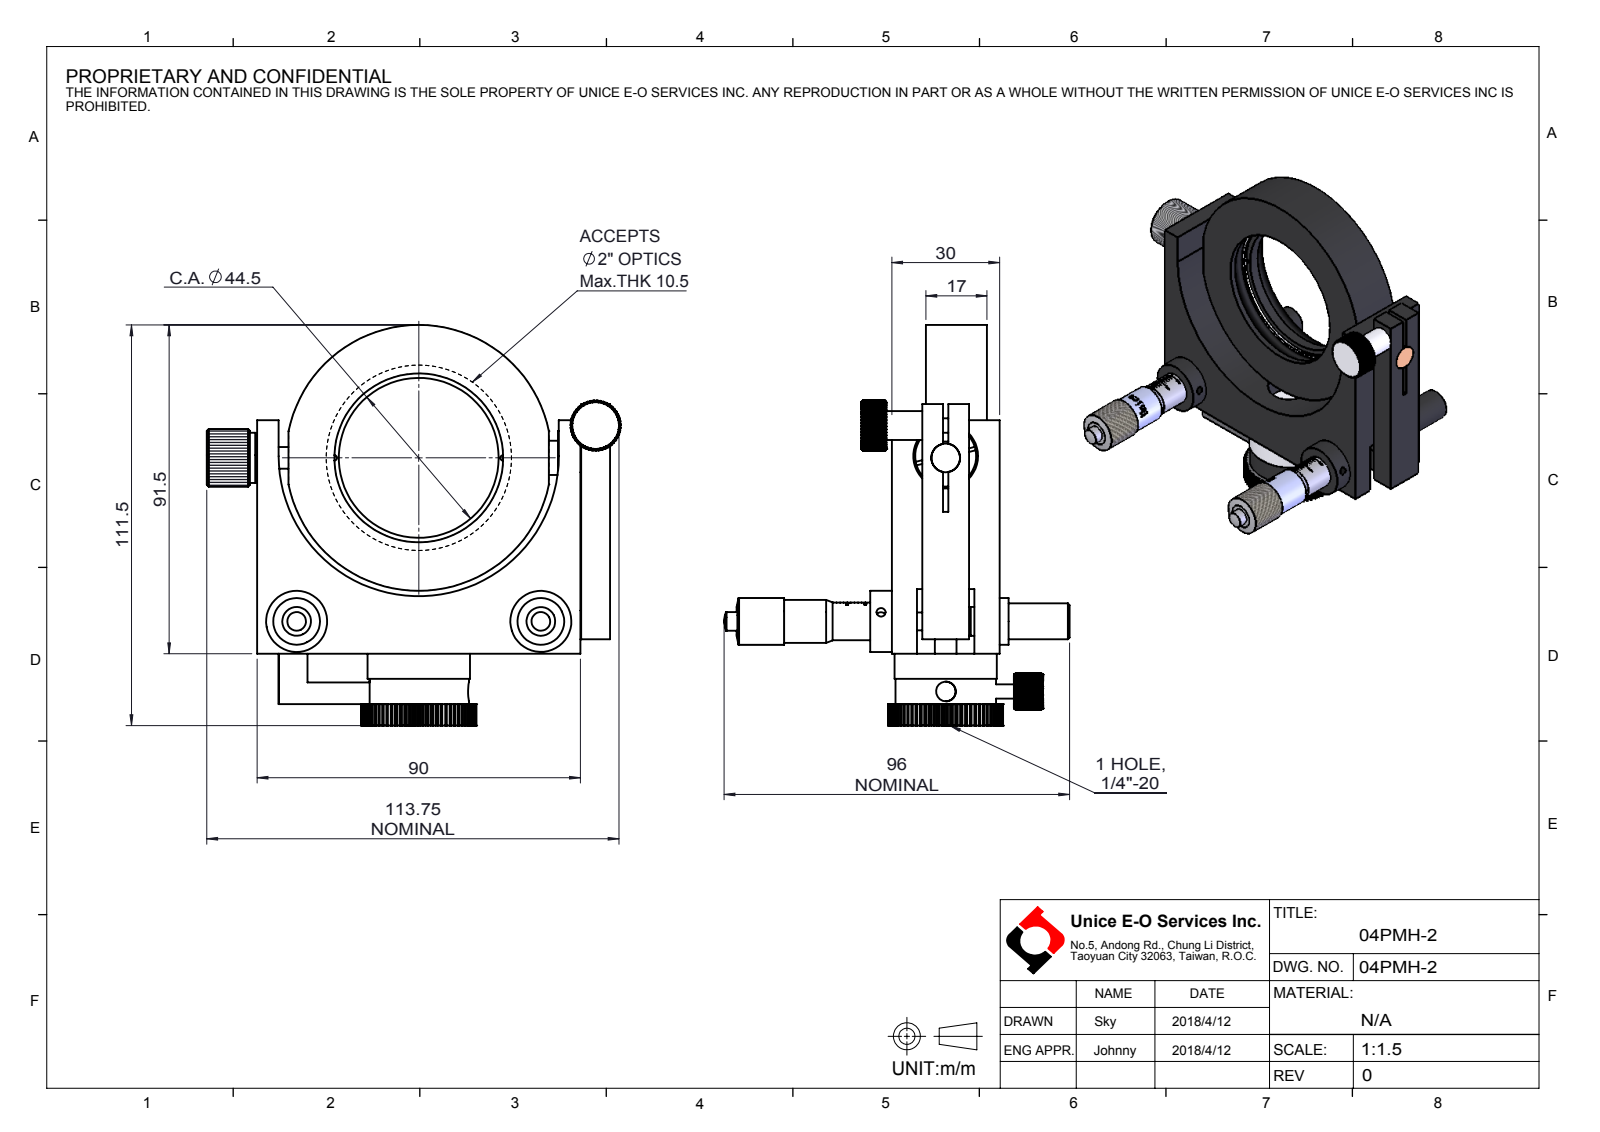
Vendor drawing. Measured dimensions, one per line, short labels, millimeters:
name: 04PMH-2
written by: SolidWorks 2016 (CONFIG_CONTROL_DESIGN)
unit: mm
bodies: 26 solids, 1785 faces (903 planar, 458 cylindrical, 424 other)
size: 115.25 × 111.5 × 97
volume: 147 397 mm³; area: 68 400 mm²
holes: 4× ⌀2.5, 4× ⌀5, 3× ⌀3.4, 3× ⌀8, 2× ⌀1.5, 2× ⌀3.3, 2× ⌀6, 2× ⌀6.3, 2× ⌀8.5, 2× ⌀9.5, 2× ⌀10.6, 2× ⌀12
bosses: 4× ⌀14, 3× ⌀17, 2× ⌀13, 2× ⌀12, 2× ⌀10.5, 2× ⌀10, 2× ⌀9.9, 2× ⌀9.2
rounds: 5× R5, 2× R5.98, 1× R7, 1× R16, 1× R39
face distances: 3.5, 9.5, 7, 6, 20.5, 17, 30, 26.5, 14, 8
hole spacings: 0.5, 11, 23.5, 56.8, 22, 27.28, 46.68, 46.72
